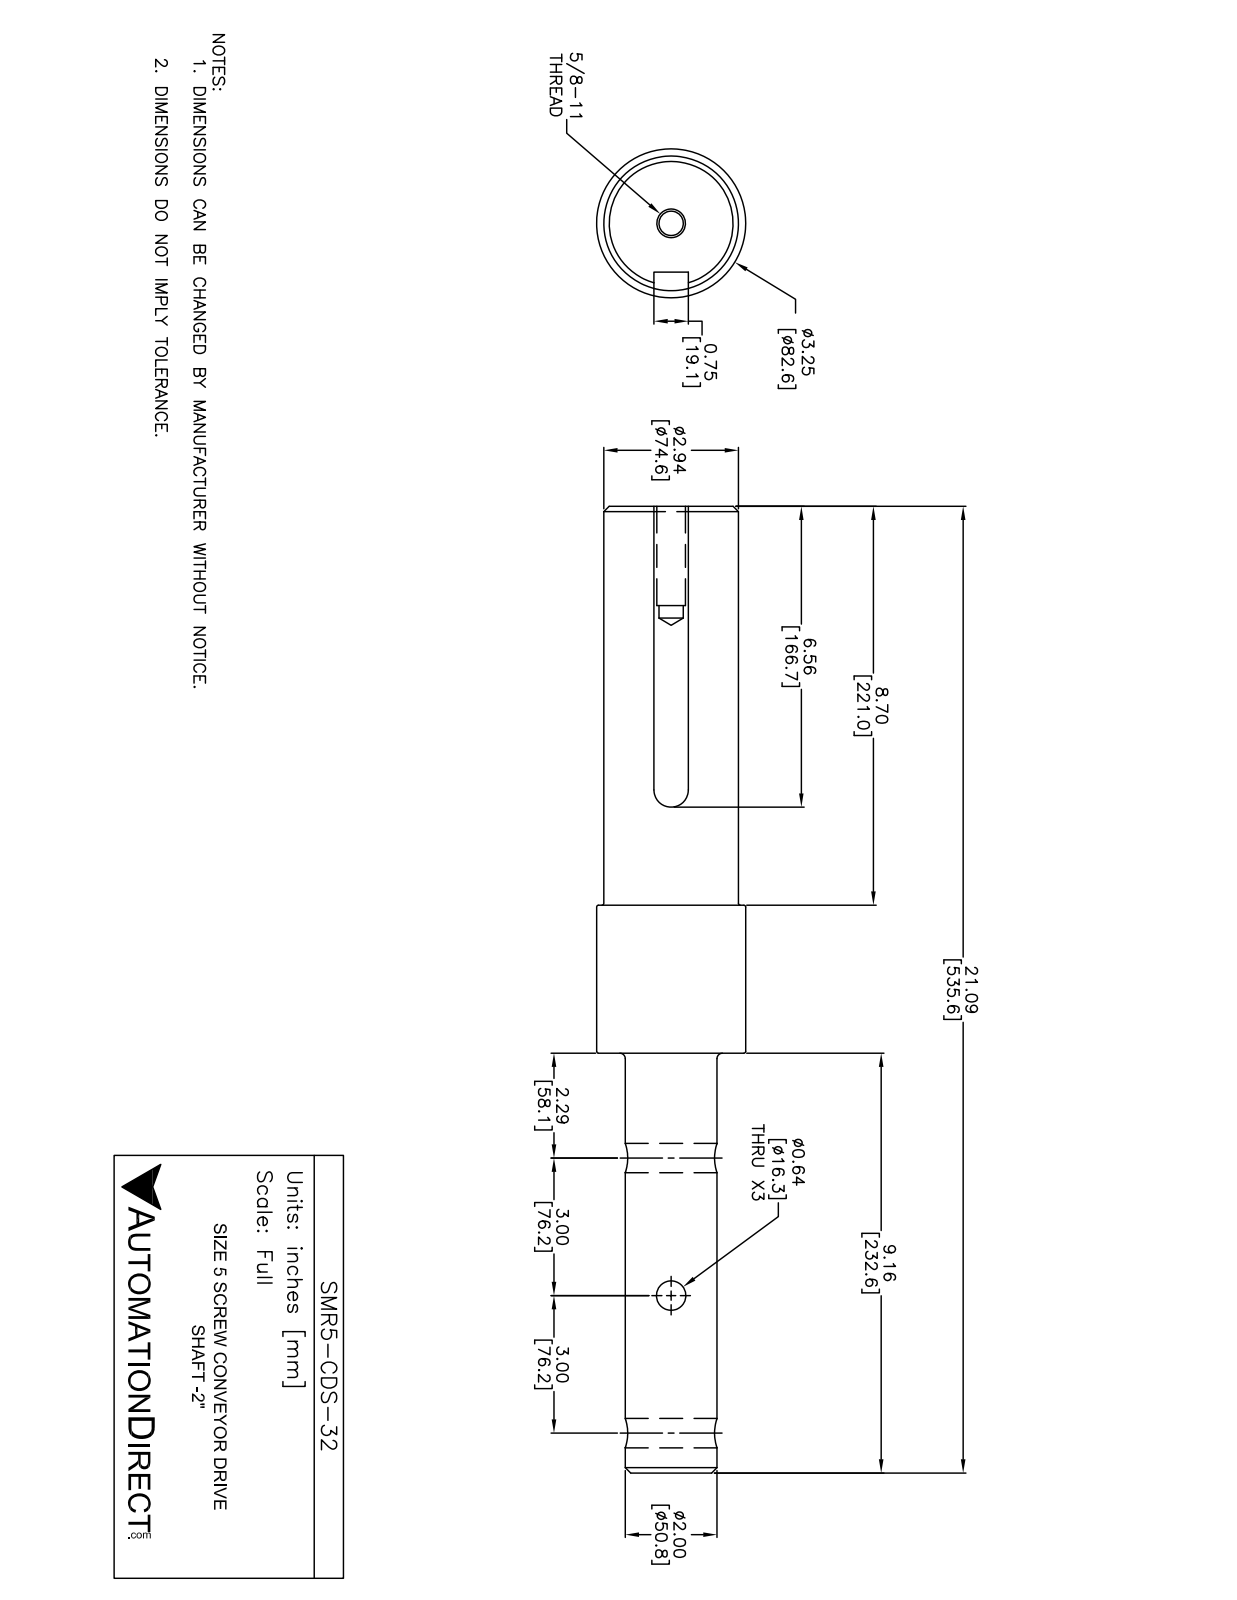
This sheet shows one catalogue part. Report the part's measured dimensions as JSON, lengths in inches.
{"part_name": "SMR5-CDS-32", "step_written_by": "SolidWorks 2016 (AUTOMOTIVE_DESIGN)", "units": "inches", "bodies": {"solids": 1, "faces": 40, "planar": 8, "cylindrical": 18, "other": 14}, "overall_size": [21.087, 3.25, 3.25], "volume_in3": 109.9, "surface_area_in2": 204.6, "round_holes": [[0.642, 3], [0.531, 1], [0.625, 1]], "round_bosses_or_shafts": [[3.25, 1], [2.937, 1], [2, 1]], "partial_cylinders_radius": [[0.375, 1]], "face_to_face_distances": [11.929, 21.087, 9.157, 0.75, 8.701, 3.228, 12.386, 2.165, 6.535, 9.764], "hole_center_spacings": [6]}
